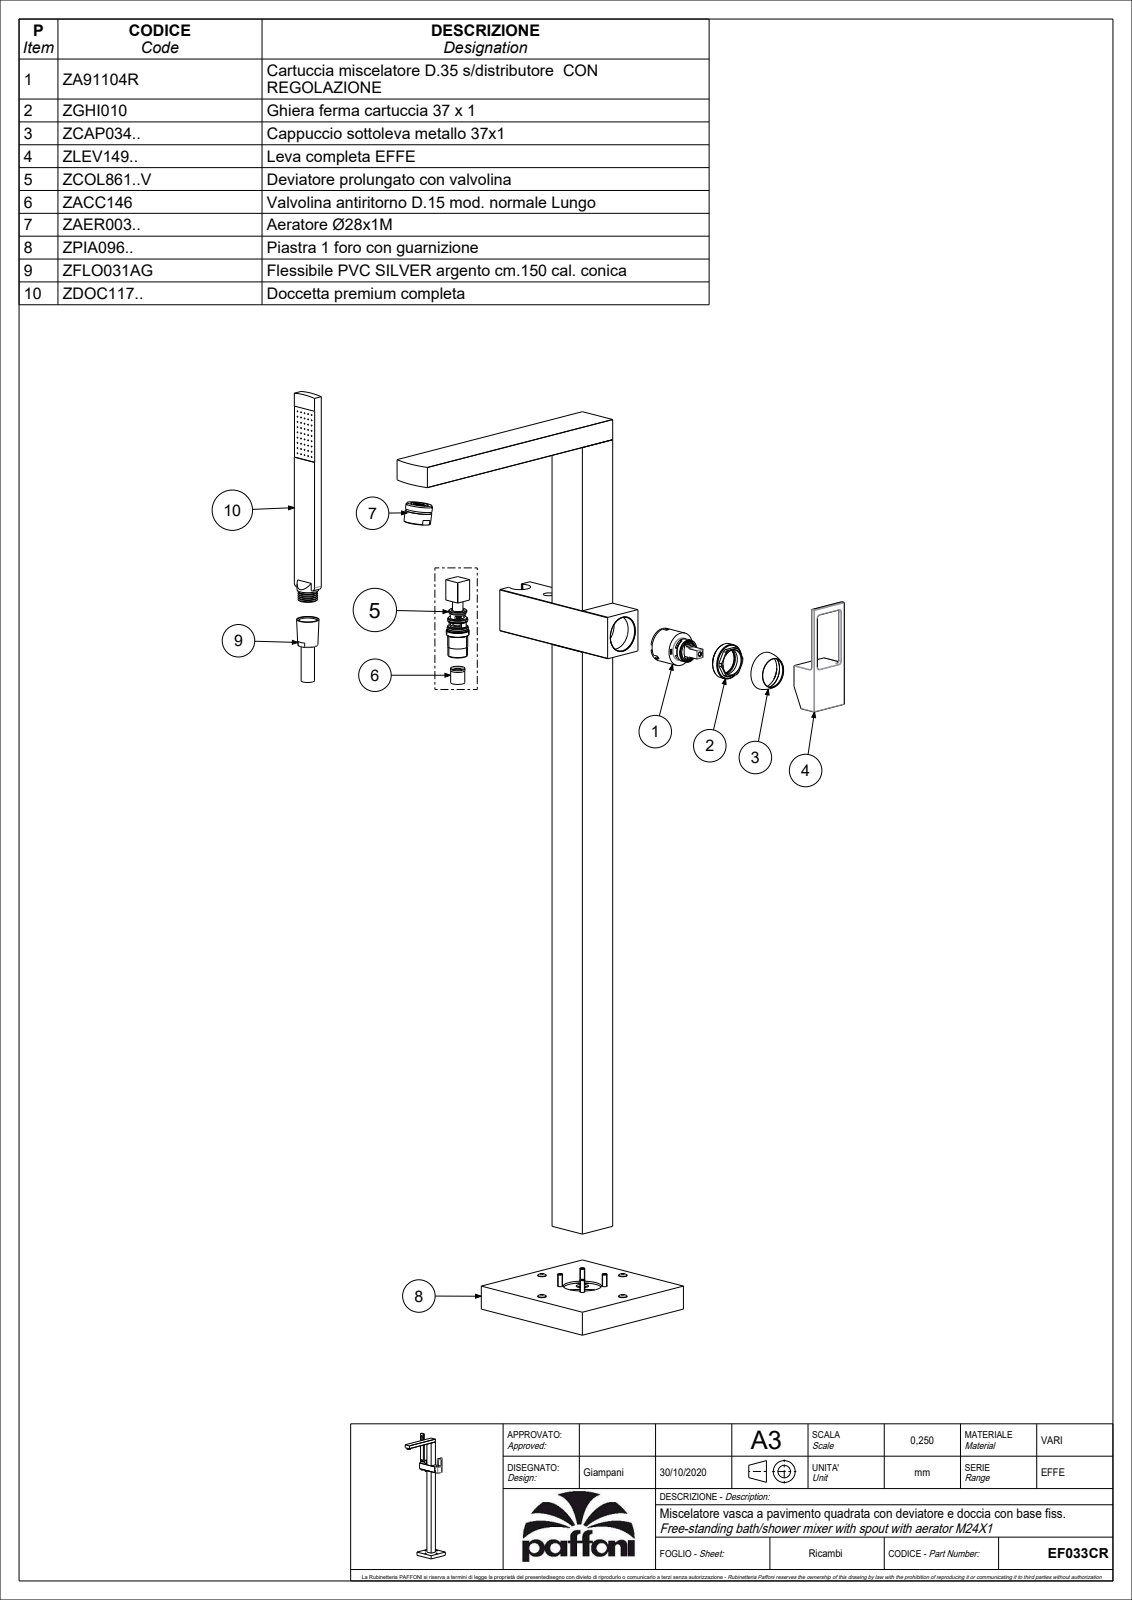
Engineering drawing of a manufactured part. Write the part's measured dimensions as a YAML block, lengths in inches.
part_name: "EF033CR"
step_written_by: "CREO PARAMETRIC BY PTC INC, 2020044 (CONFIG_CONTROL_DESIGN)"
units: inches
bodies: {solids: 7, faces: 3468, planar: 2576, cylindrical: 514, other: 378}
overall_size: [36.89, 13.012, 7.839]
volume: 71.76
surface_area: 957.8
round_holes:
  - {diameter: 0.236, count: 7}
  - {diameter: 0.165, count: 6}
  - {diameter: 0.512, count: 5}
  - {diameter: 0.13, count: 4}
  - {diameter: 0.244, count: 4}
  - {diameter: 0.315, count: 4}
  - {diameter: 0.433, count: 4}
  - {diameter: 0.177, count: 3}
  - {diameter: 0.394, count: 3}
  - {diameter: 0.157, count: 2}
  - {diameter: 0.197, count: 2}
  - {diameter: 0.354, count: 2}
round_bosses_or_shafts:
  - {diameter: 0.079, count: 11}
  - {diameter: 0.354, count: 8}
  - {diameter: 0.197, count: 4}
  - {diameter: 0.295, count: 3}
  - {diameter: 0.63, count: 2}
  - {diameter: 0.394, count: 2}
  - {diameter: 0.335, count: 2}
  - {diameter: 0.331, count: 2}
partial_cylinders:
  - {radius: 0.02, count: 37}
  - {radius: 0.118, count: 5}
  - {radius: 0.012, count: 4}
  - {radius: 0.157, count: 3}
  - {radius: 0.039, count: 2}
  - {radius: 0.276, count: 1}
  - {radius: 0.366, count: 1}
  - {radius: 0.384, count: 1}
face_to_face_distances: [0.059, 1.713, 1.772, 1.654, 0.079, 34.528, 0.984, 0.866, 0.906, 2.067]
hole_center_spacings: [2.669, 0.74, 0.919, 1.043, 1.146, 1.299, 1.587, 2.306]
